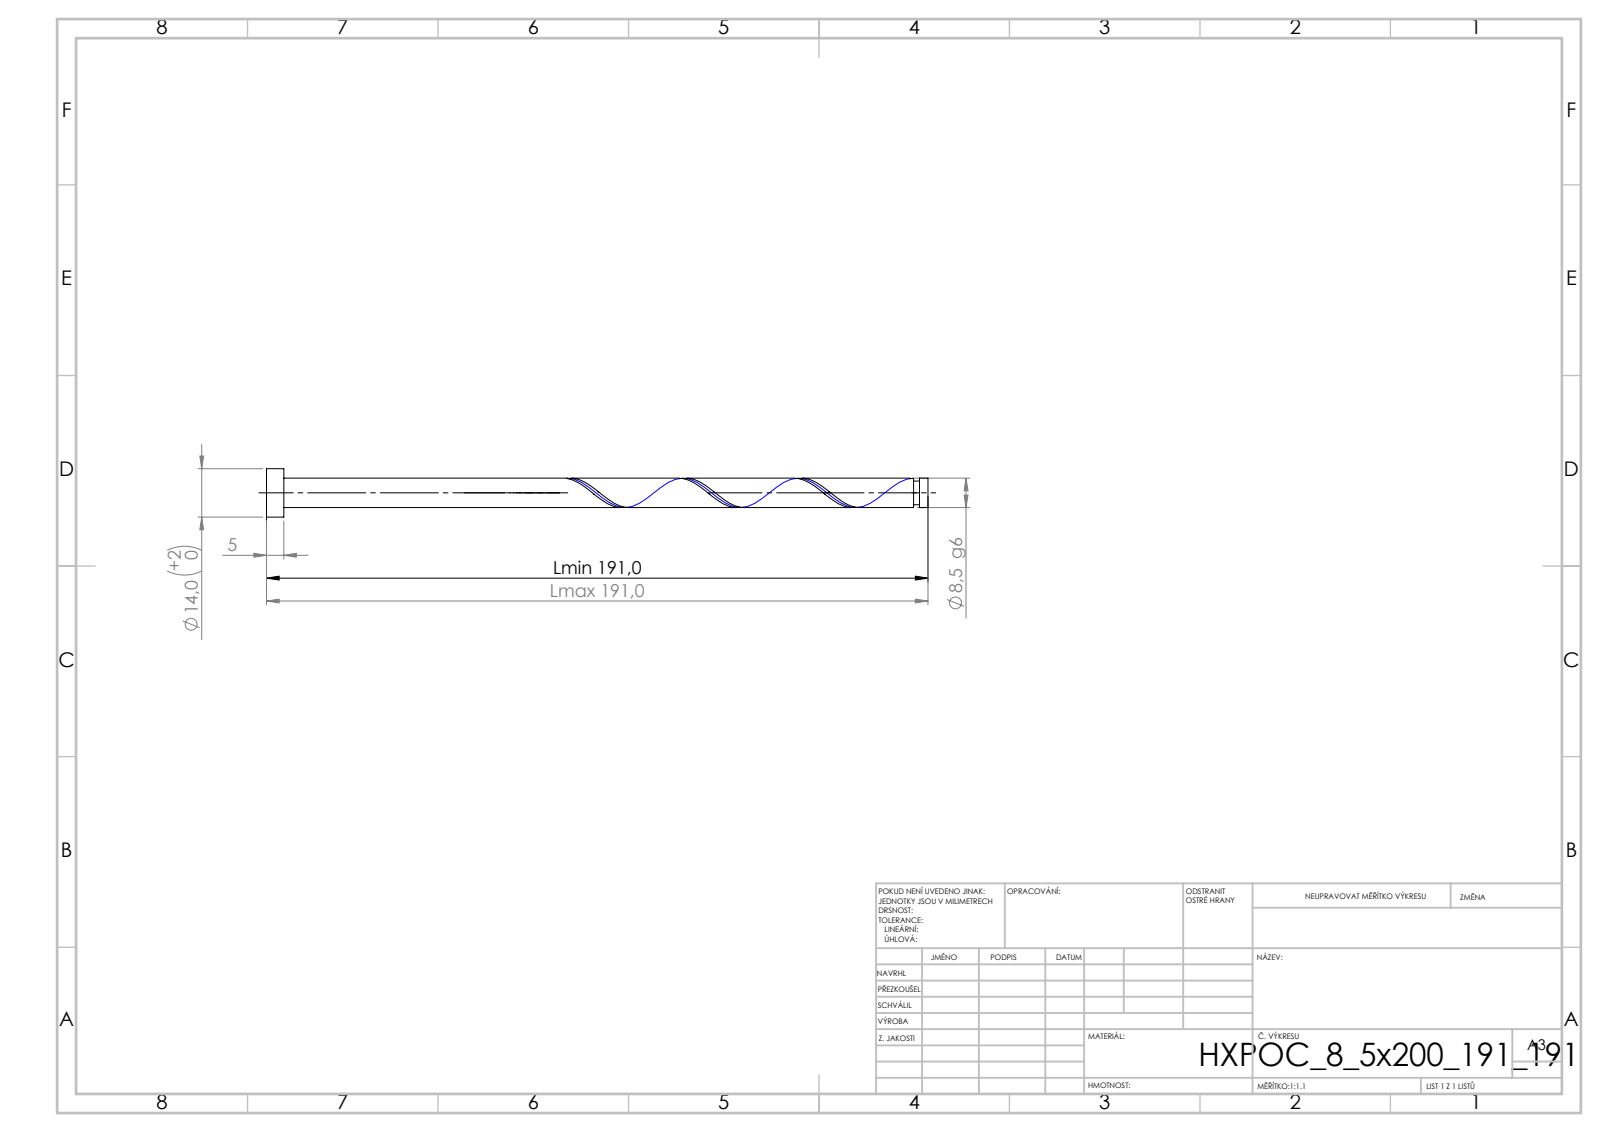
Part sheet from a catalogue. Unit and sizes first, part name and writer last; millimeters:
Units: millimetres
Overall size (bounding box): 191 × 14 × 14
Round bosses / shafts (diameter × count): ⌀14 ×1, ⌀8.5 ×1, ⌀6.8 ×1
Main face-to-face distances: 5, 191, 186, 188.55, 183.55, 2.45, 186.85, 181.85, 1.7, 4.15
Volume: 11 181 mm³ · Surface area: 5 640 mm²
Bodies: 1 solid, 21 faces (6 planar, 14 cylindrical, 1 other)
STEP written by: SolidWorks 2019 (CONFIG_CONTROL_DESIGN)
